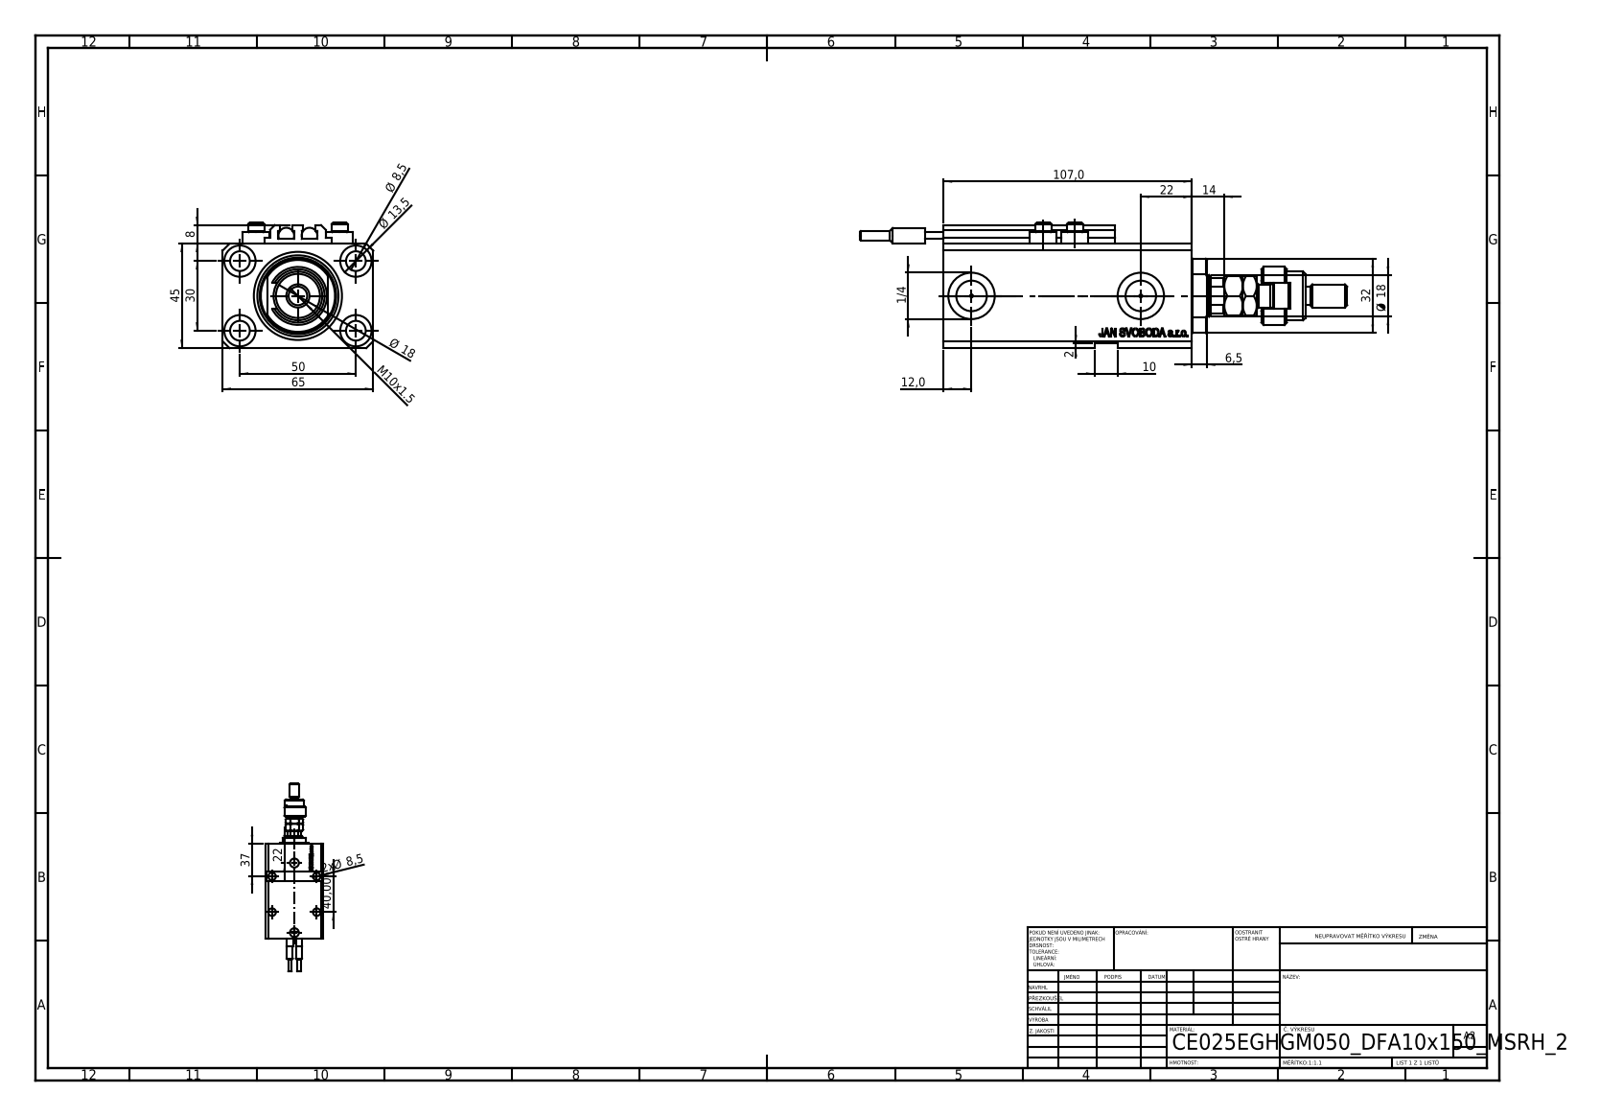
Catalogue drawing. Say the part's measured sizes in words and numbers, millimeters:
The part is named "V250CE_VC_E; SWITCH_V250CE; V250CE_E_Body; ALLEN BOLT V250CE (+3 more)". Its 3-D file was written by "SolidWorks 2019 (CONFIG_CONTROL_DESIGN)". It is 12 solids with 1224 faces: 571 planar, 171 cylindrical and 482 other. Overall it measures 210 by 79.5 by 69.12 millimeters. Its volume is 287 581 cubic millimeters and its surface area 84 073 square millimeters. Round holes: 9 of diameter 8.5, 4 of diameter 1.25, 4 of diameter 4, 4 of diameter 13.5, 2 of diameter 10, 2 of diameter 13.16, 2 of diameter 20, 1 of diameter 18, 1 of diameter 38. Round bosses or shafts: 4 of diameter 11.6, 4 of diameter 7, 2 of diameter 6.8, 2 of diameter 6.5, 2 of diameter 4, 1 of diameter 25, 1 of diameter 21, 1 of diameter 16. Partial cylindrical surfaces (rounded edges, fillets, slot ends): 10 of radius 0.2, 1 of radius 5.5, 1 of radius 8.5, 1 of radius 8.75, 1 of radius 16. The main face-to-face distances are 45, 65, 14, 2, 93, 47, 3, 107, 5, 2.5. The hole center spacings are 29.15, 50, 13.6, 14.76, 15.12, 27.51, 27.89, 30.
